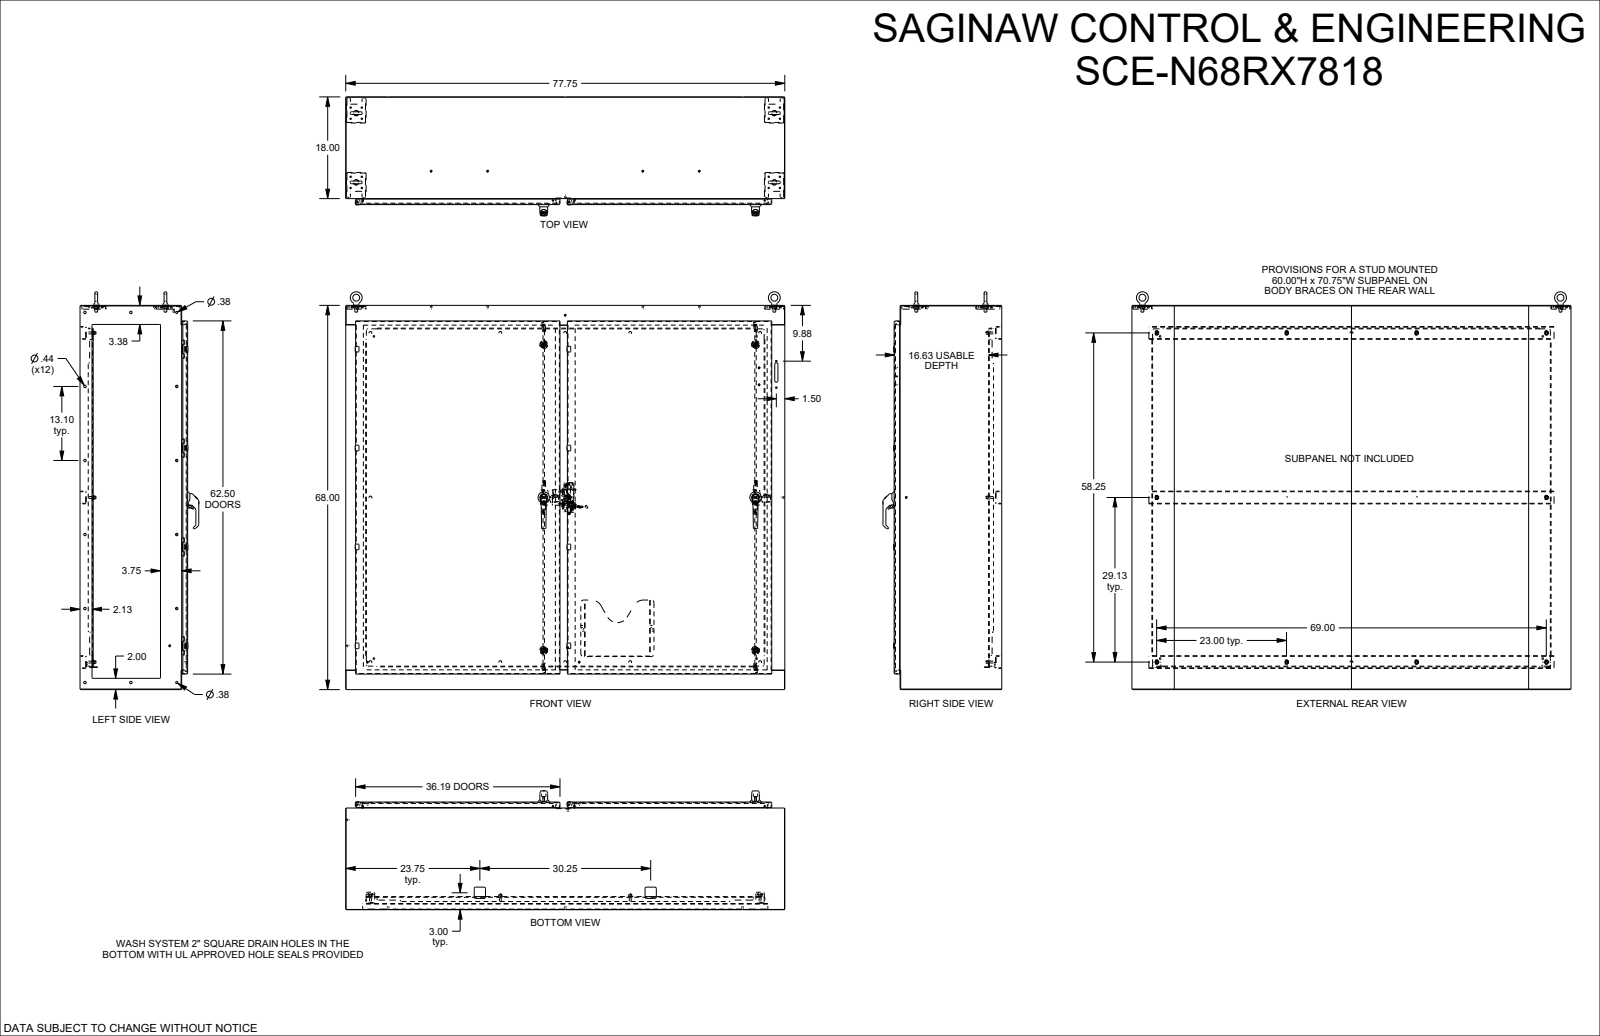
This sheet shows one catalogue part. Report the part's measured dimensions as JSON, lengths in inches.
{"part_name": "SCE-N68RX7818", "step_written_by": "SolidWorks 2023 (AUTOMOTIVE_DESIGN)", "units": "inches", "bodies": {"solids": 50, "faces": 7518, "planar": 3073, "cylindrical": 2565, "other": 1880}, "overall_size": [77.75, 70.945, 21.046], "volume_in3": 1876, "surface_area_in2": 35644, "round_holes": [[0.25, 22], [0.375, 18], [0.244, 16], [0.437, 12], [0.04, 8], [0.17, 8], [0.205, 8], [0.205, 8], [0.218, 8], [0.344, 8], [0.115, 4], [0.256, 4]], "round_bosses_or_shafts": [[0.17, 24], [0.25, 19], [0.24, 16], [0.196, 10], [1.4, 4], [1.173, 4], [0.6, 4], [0.341, 4]], "partial_cylinders_radius": [[0.03, 214], [0.015, 166], [0.125, 96], [0.062, 70], [0.02, 57], [0.04, 57], [0.25, 49], [0.02, 48]], "face_to_face_distances": [0.104, 18.954, 18.85, 19.058, 67.896, 17.896, 1.058, 68, 67.792, 17.792], "hole_center_spacings": [13.1, 20.873, 17.5, 26.2, 30.83, 35, 37.5, 16.25]}
